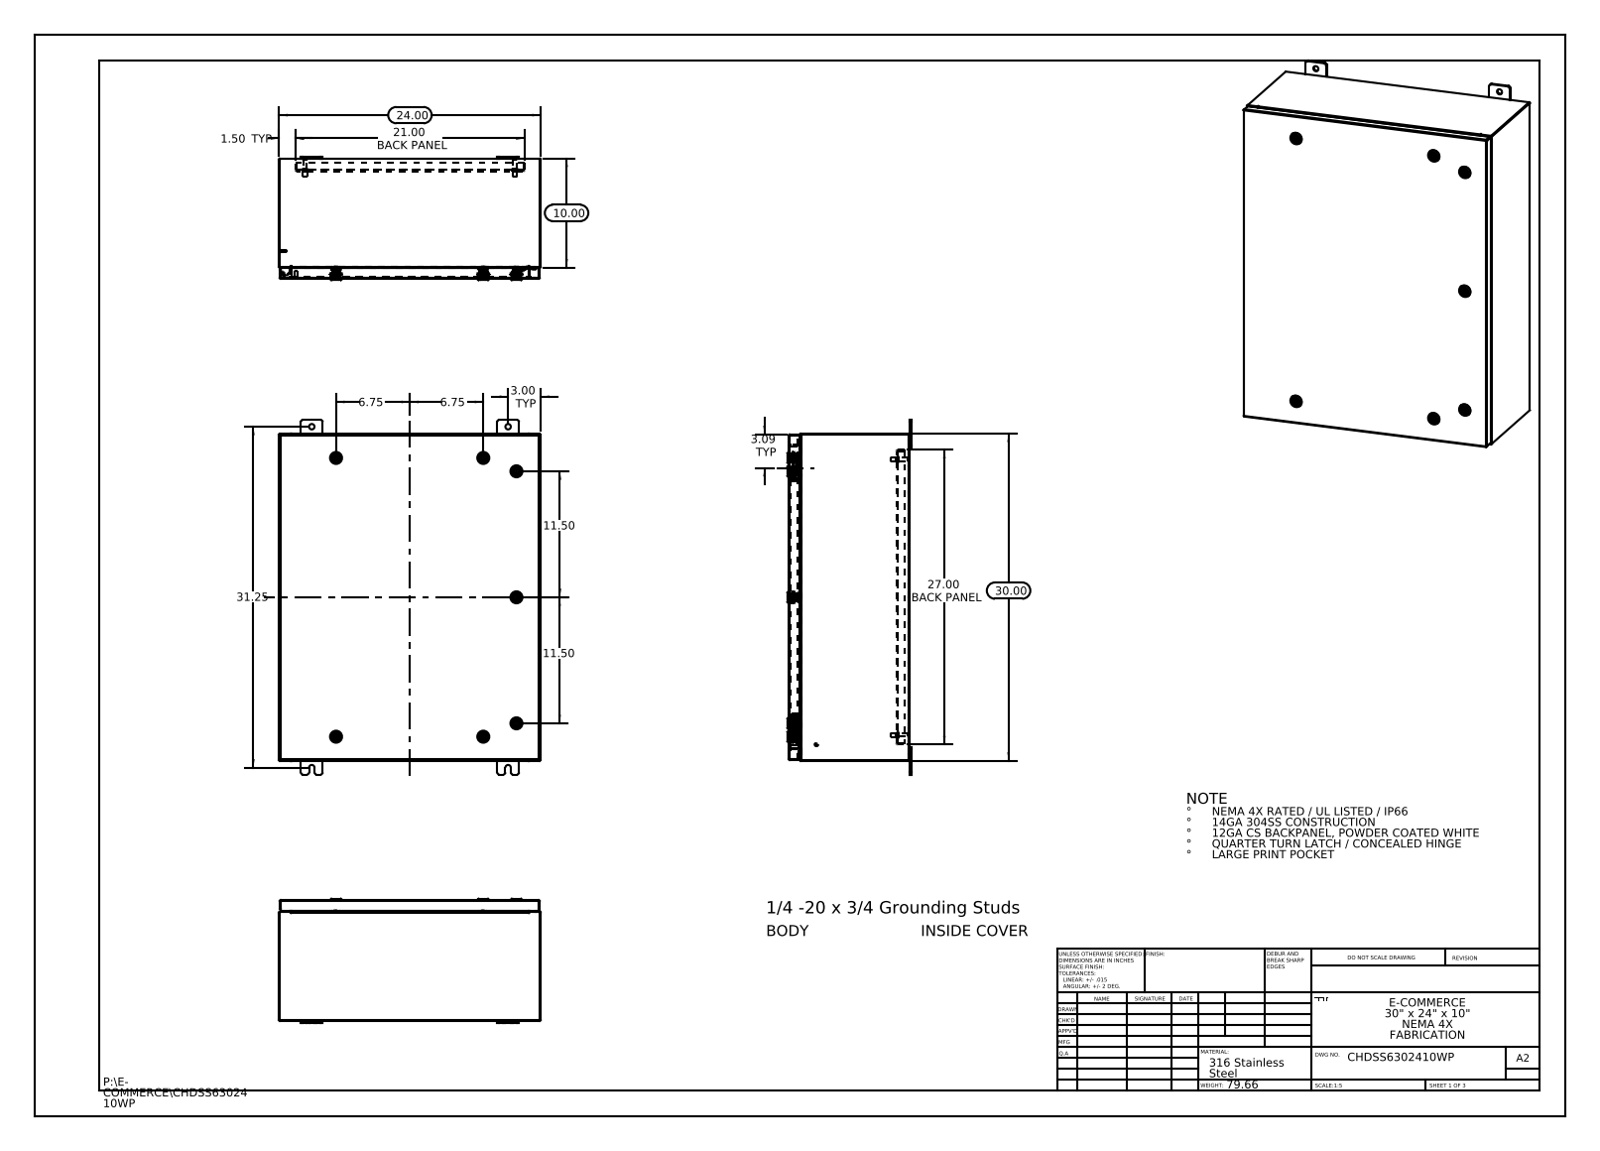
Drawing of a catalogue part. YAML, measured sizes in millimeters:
part_name: "Washer-221320-IB-Industrilas_Washer-221320-IB-Industrilas; Concealed Hinge enclosure side; CHDSS6302410WP Top; HW-CLH-E5-8004_Cam-232112-U-Industrilas (+8 more)"
step_written_by: "SolidWorks 2013 (CONFIG_CONTROL_DESIGN)"
units: millimeters
bodies: {solids: 61, faces: 6252, planar: 1822, cylindrical: 1948, other: 2482}
overall_size: [825.5, 609.6, 288.4]
volume: 4638000
surface_area: 4551000
round_holes:
  - {diameter: 12.7, count: 8}
  - {diameter: 5, count: 7}
  - {diameter: 10, count: 7}
  - {diameter: 10.2, count: 7}
  - {diameter: 16, count: 7}
  - {diameter: 20, count: 7}
  - {diameter: 3.5, count: 4}
  - {diameter: 5.4, count: 1}
round_bosses_or_shafts:
  - {diameter: 6, count: 9}
  - {diameter: 28, count: 7}
  - {diameter: 19.8, count: 7}
  - {diameter: 15.9, count: 7}
  - {diameter: 15.5, count: 7}
  - {diameter: 13.5, count: 7}
  - {diameter: 10, count: 7}
  - {diameter: 2.9, count: 7}
partial_cylinders:
  - {radius: 0.2, count: 231}
  - {radius: 3, count: 231}
  - {radius: 0.7, count: 84}
  - {radius: 0.5, count: 28}
  - {radius: 5, count: 28}
  - {radius: 4.8, count: 24}
  - {radius: 0.3, count: 22}
  - {radius: 2.2, count: 18}
face_to_face_distances: [1.9, 1.9, 279.7, 277.7, 277.8, 275.9, 2.6, 607.7, 25.4, 27.3]
hole_center_spacings: [17.5, 47.2, 83.2, 293.4, 342.9, 421.2, 457.2, 489]
